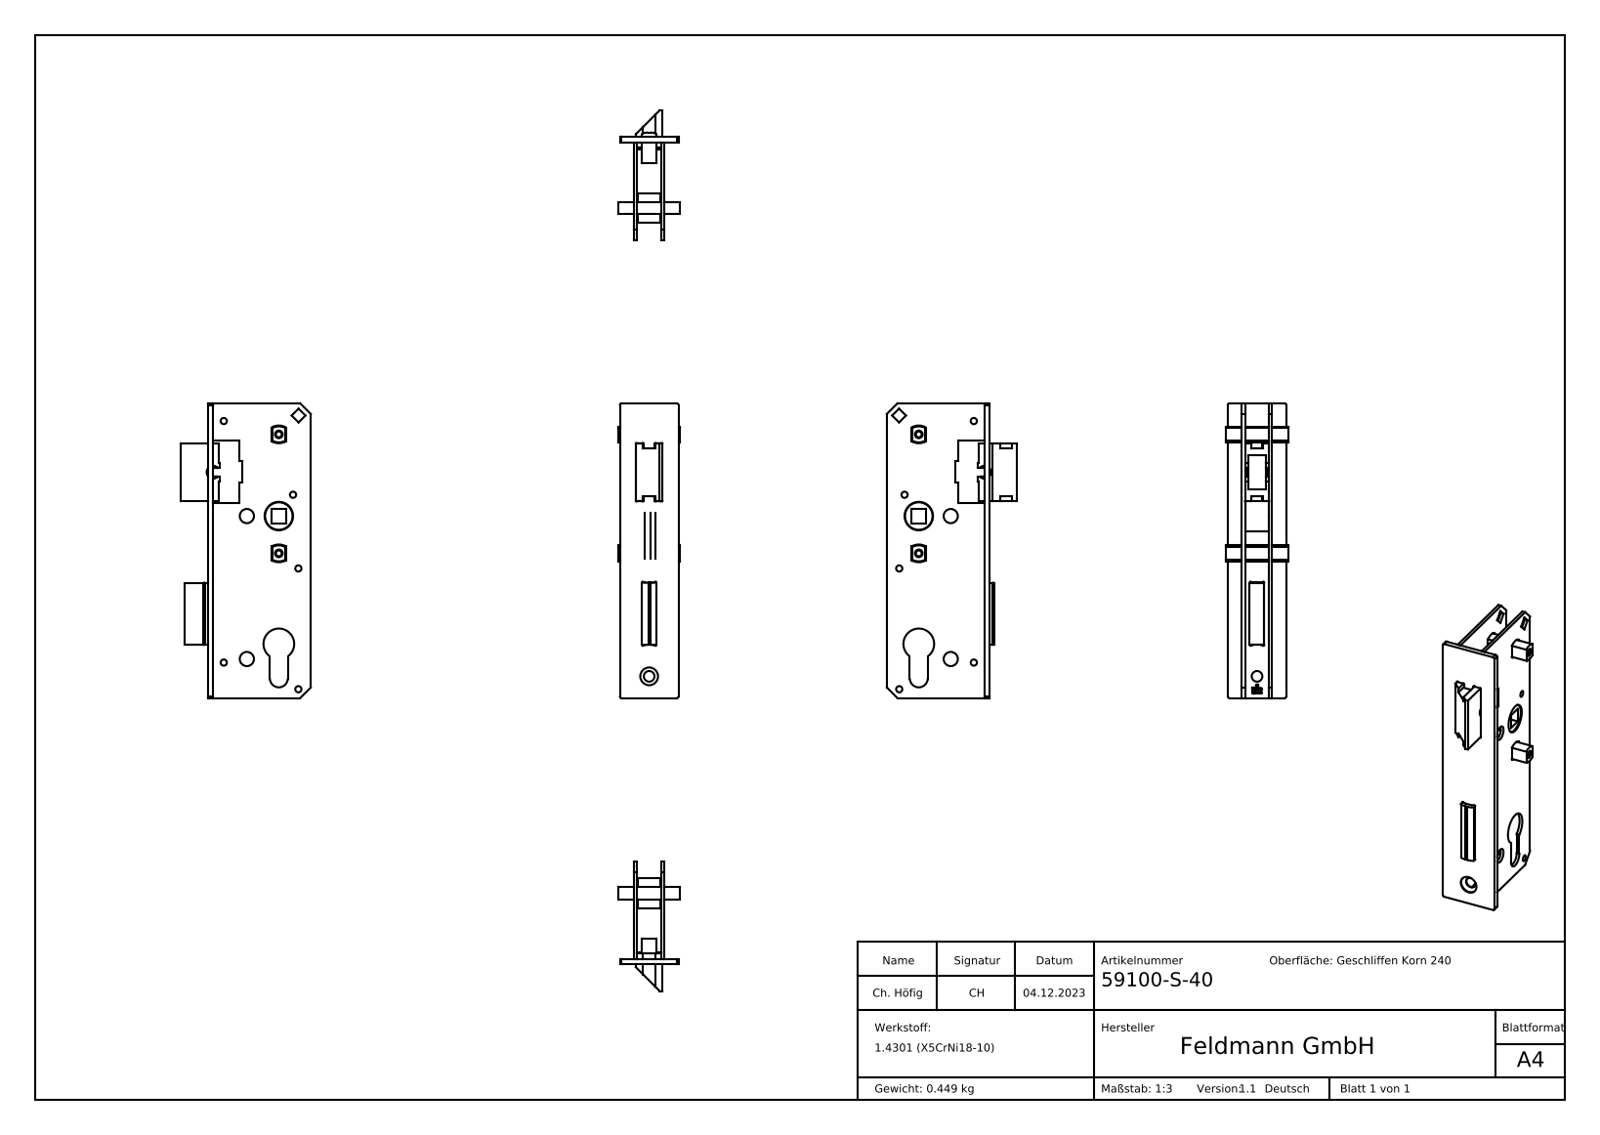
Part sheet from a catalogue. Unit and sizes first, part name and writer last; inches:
Units: inches
Overall size (bounding box): 6.535 × 2.874 × 1.378
Round holes (diameter × count): ⌀0.138 ×5, ⌀0.13 ×2, ⌀0.315 ×2, ⌀0.236 ×1, ⌀0.394 ×1, ⌀0.63 ×1, ⌀0.681 ×1
Round bosses / shafts (diameter × count): ⌀0.669 ×1, ⌀0.61 ×1
Partial cylindrical surfaces — rounded edges, fillets, slot ends (radius × count): R0.012 ×8, R0.024 ×8, R0.02 ×4, R0.039 ×4, R0.173 ×4, R0.295 ×4, R0.315 ×4, R0.094 ×1
Main face-to-face distances: 0.6, 0.069, 0.669, 0.531, 0.118, 0.315, 0.455, 0.384, 0.915, 0.984
Hole centre spacings: 0.518, 0.547, 0.568, 0.709, 0.784, 0.827, 1.089, 1.093
Volume: 3.458 in³ · Surface area: 83.65 in²
Bodies: 8 solids, 481 faces (270 planar, 71 cylindrical, 140 other)
Part name (STEP PRODUCT): Schlosskasten Teil4 Konfig_59XXX-240 Teil4; 59100-S-40; Schlosskasten Teil3 Konfig_59XXX-240 Teil3; Schlosskasten Teil5 Konfig_59XXX-240 Teil5 (+1 more)
STEP written by: SolidWorks 2018 (CONFIG_CONTROL_DESIGN)
